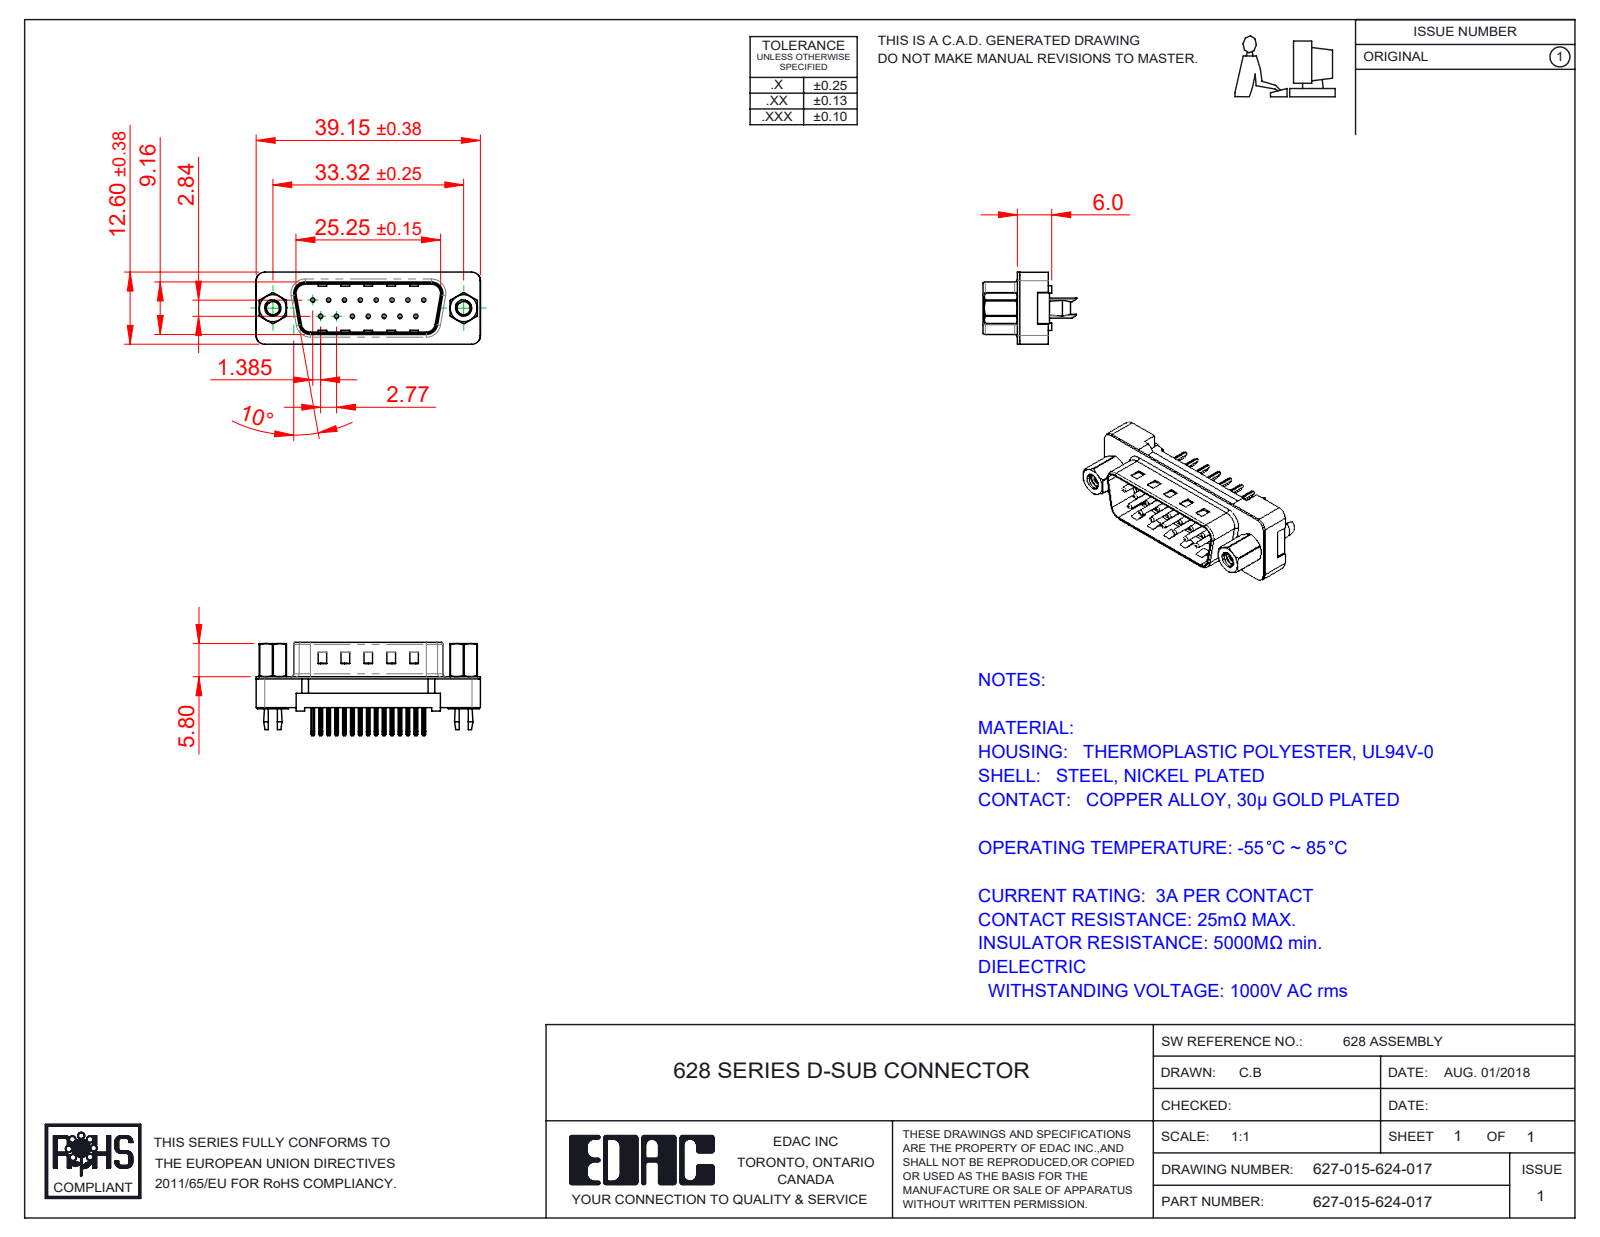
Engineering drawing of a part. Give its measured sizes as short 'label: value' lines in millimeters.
name: 627 4-40 Hex Standoff; 627 PB Contact Row 2_24; 627-015-624-017; 627 Plastic Body Housing_15 Contacts (+3 more)
written by: SolidWorks 2020 (CONFIG_CONTROL_DESIGN)
unit: mm
bodies: 21 solids, 1303 faces (773 planar, 406 cylindrical, 124 other)
size: 39.19 × 16.3 × 12.6
volume: 2 235 mm³; area: 4 910 mm²
holes: 15× ⌀0.35, 15× ⌀0.85, 2× ⌀2.26, 2× ⌀2.29, 2× ⌀4, 2× ⌀4.8, 2× ⌀5
bosses: 15× ⌀0.75, 2× ⌀4.9, 2× ⌀2.79
rounds: 30× R0.25, 15× R0.12, 8× R0.5, 8× R1.5, 4× R0.9, 4× R1.6, 4× R2, 2× R0.4
face distances: 0.4, 2.5, 5.4, 8.76, 5, 2.9, 1.58, 9.02, 6.5, 0.68
hole spacings: 3.16, 2.77, 5.54, 8.31, 5.03, 7.48, 11.08, 5.04
